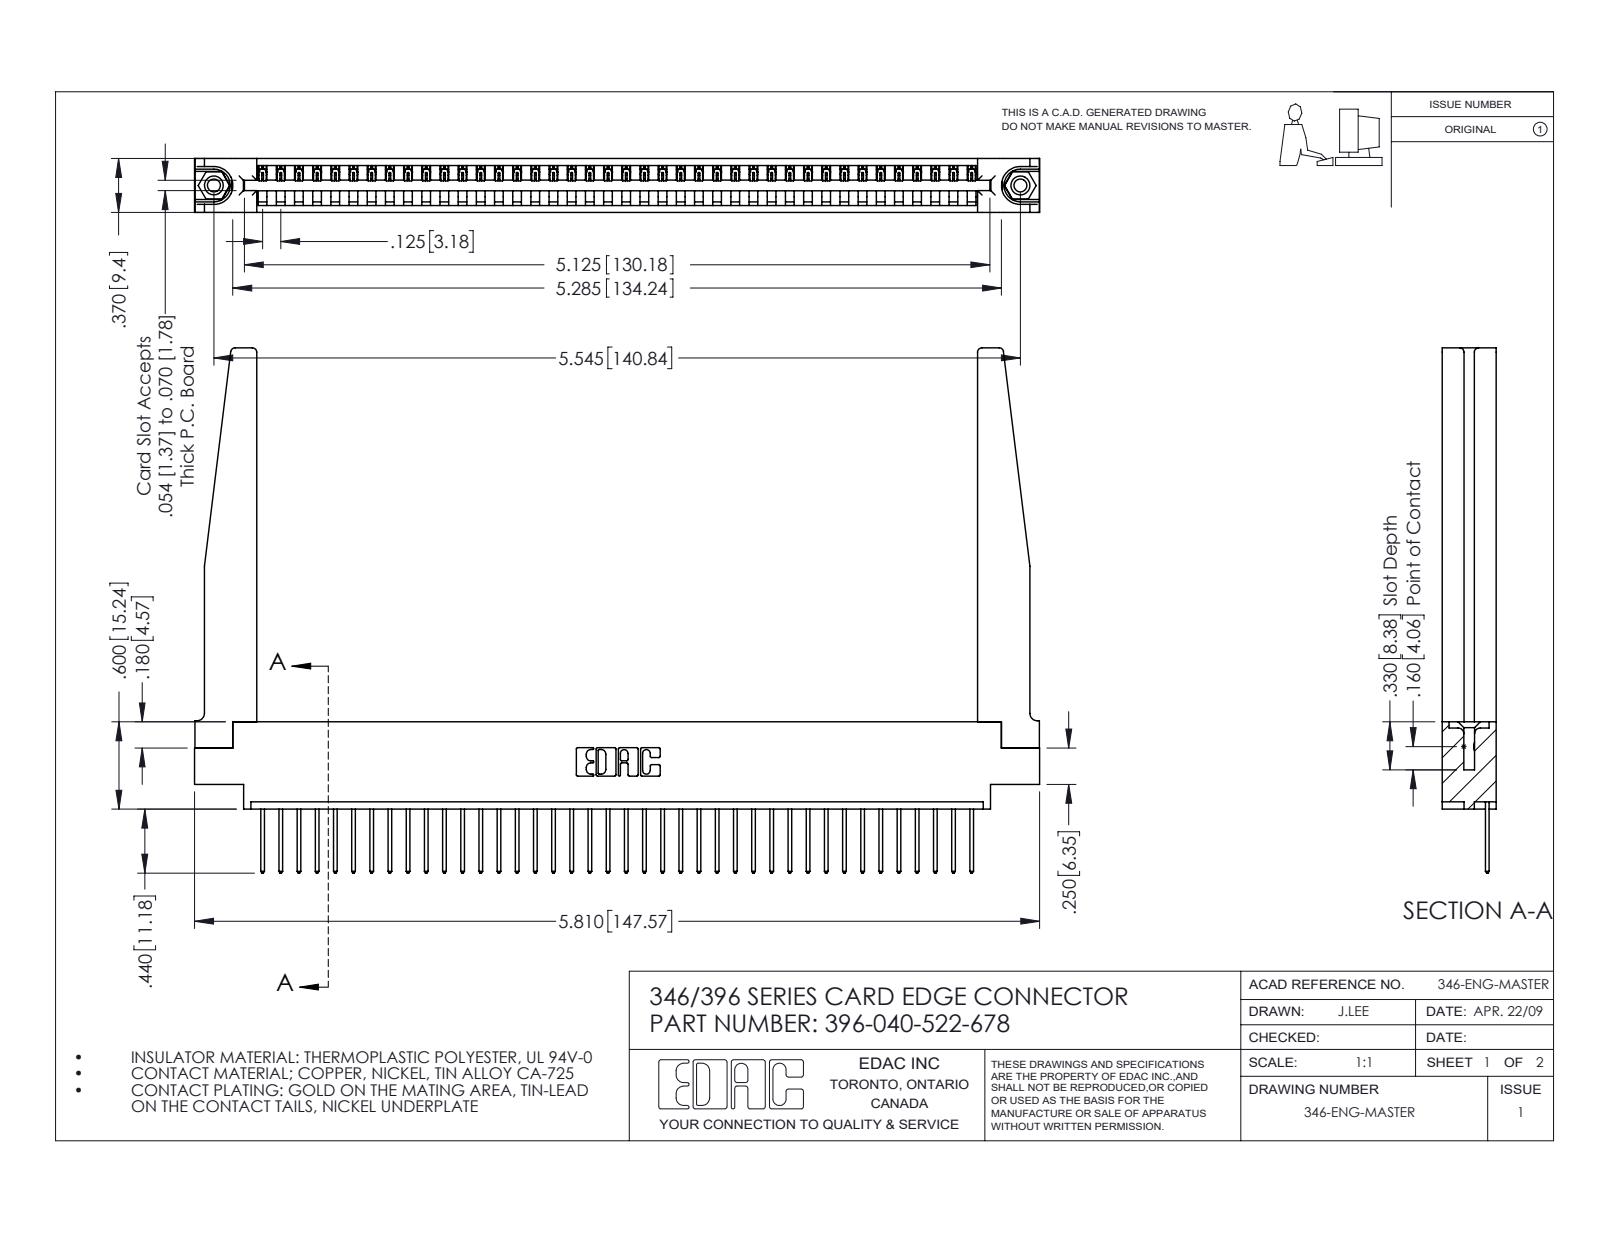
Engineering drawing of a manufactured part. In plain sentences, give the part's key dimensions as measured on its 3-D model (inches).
The part is named "346-220-078_345-220-078; 396-040-522-678; 345-250-001_345-250-001-102; 345-292-001_345-293-122 (+1 more)". Its 3-D file was written by "SolidWorks 2016 (CONFIG_CONTROL_DESIGN)". It is 45 solids with 2680 faces: 1822 planar, 806 cylindrical and 52 other. Overall it measures 5.81 by 3.61 by 0.37 inches. Its volume is 1.274 cubic inches and its surface area 37.63 square inches. Round holes: 2 of diameter 0.089, 2 of diameter 0.125, 2 of diameter 0.156, 1 of diameter 0.064. Round bosses or shafts: 2 of diameter 0.155. Partial cylindrical surfaces (rounded edges, fillets, slot ends): 80 of radius 0.006, 80 of radius 0.01, 22 of radius 0.01, 8 of radius 0.03, 6 of radius 0.007, 6 of radius 0.031, 3 of radius 0.026, 2 of radius 0.031. The main face-to-face distances are 0.37, 0.048, 0.322, 0.072, 0.148, 0.25, 0.15, 0.298, 0.025, 0.222. The hole center spacings are 0.246, 5.336, 5.545.
